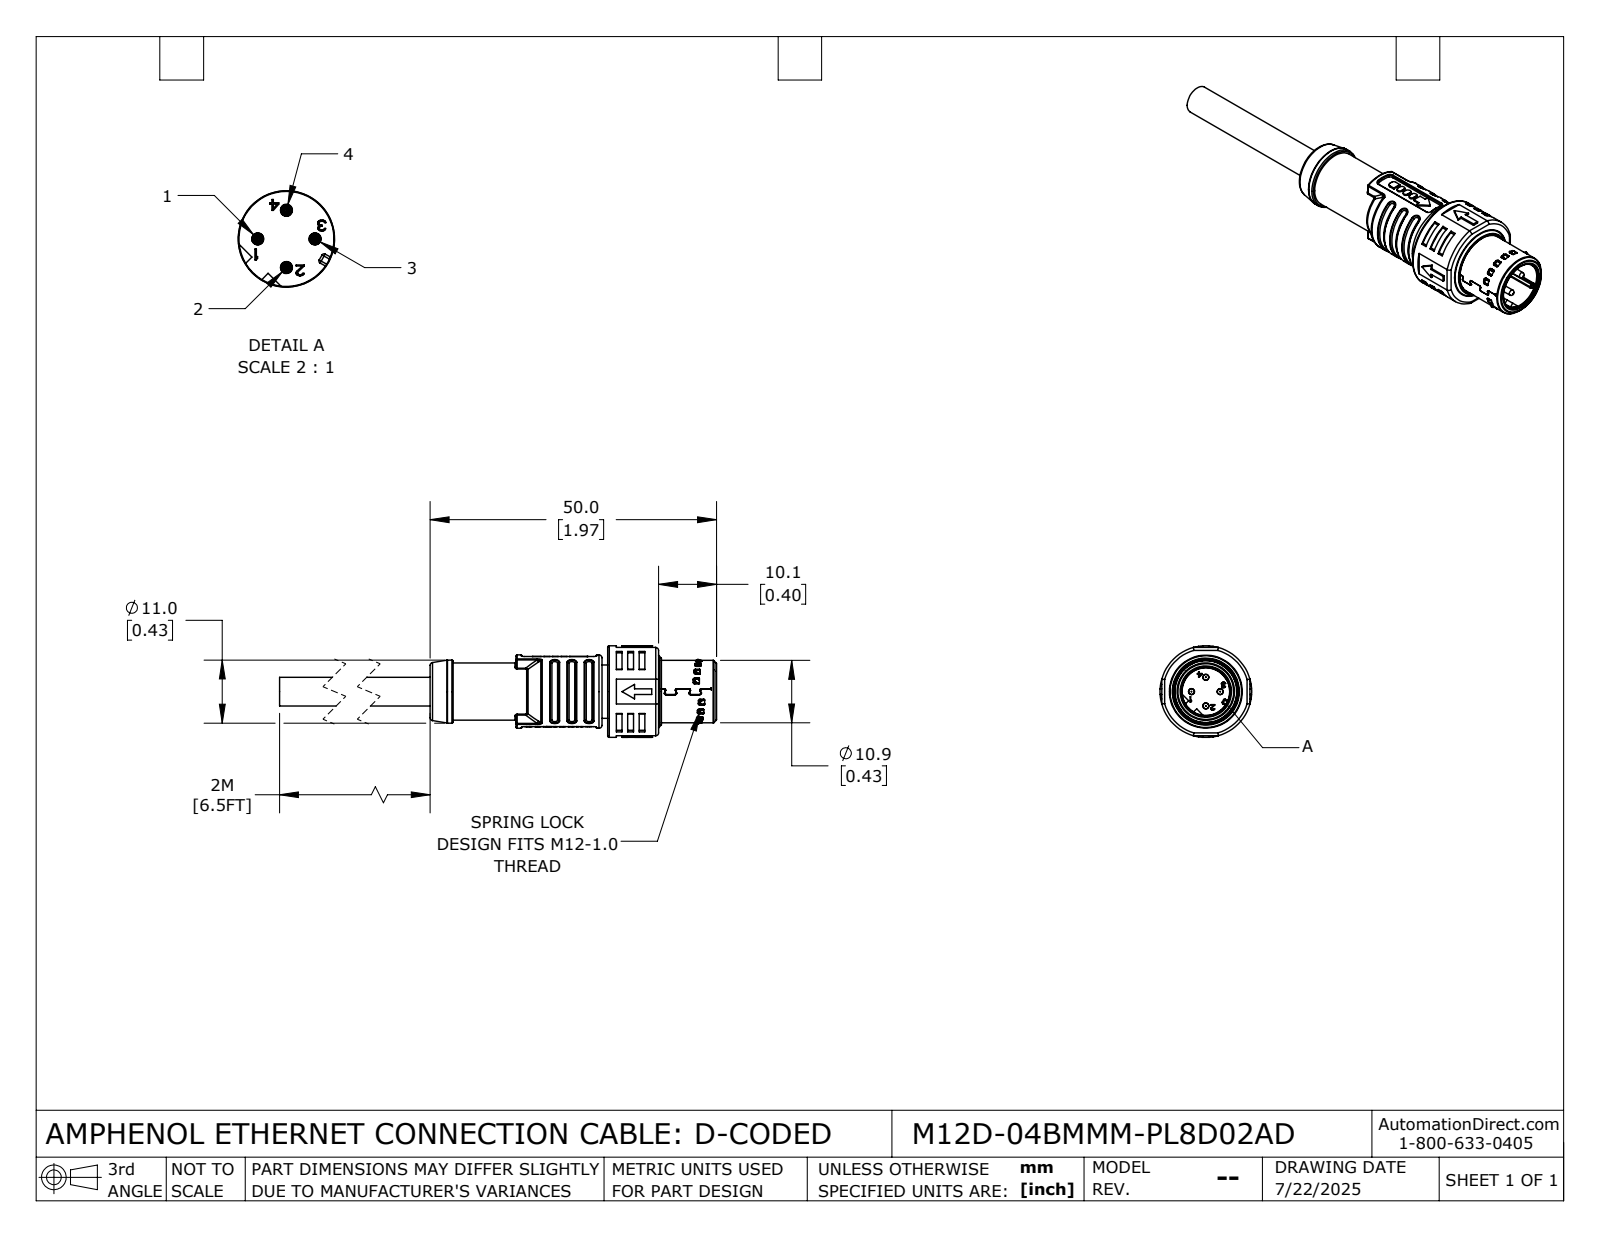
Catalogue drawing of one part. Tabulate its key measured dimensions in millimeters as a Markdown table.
| quantity | value |
| --- | --- |
| part name | M12D-04BMMM-PL8D02AD |
| STEP written by | SolidWorks 2024 (CONFIG_CONTROL_DESIGN) |
| units | millimeters |
| bodies | 1 solid, 2139 faces (996 planar, 644 cylindrical, 499 other) |
| overall size | 80 × 16 × 16 |
| volume | 5 399 mm³ |
| surface area | 5 961 mm² |
| round holes (diameter × count) | 1.05 × 4, 8.3 × 1, 9 × 1, 10.15 × 1, 10.5 × 1, 10.9 × 1, 11.5 × 1, 11.8 × 1, 14.2 × 1 |
| round bosses / shafts (diameter × count) | 1 × 4, 16 × 1, 14.1 × 1, 12.8 × 1, 12.4 × 1, 11 × 1, 10.45 × 1, 10.4 × 1 |
| partial cylindrical surfaces (radius × count) | 0.2 × 119, 0.25 × 66, 0.3 × 64, 0.15 × 44, 0.5 × 38, 0.13 × 12, 0.7 × 11, 0.1 × 7 |
| main face-to-face distances | 1, 30, 10.1, 8.9, 2.5, 1.2, 8.6, 32.5, 15.4, 1.5 |
| hole center spacings | 2.5, 3.54, 5 |
